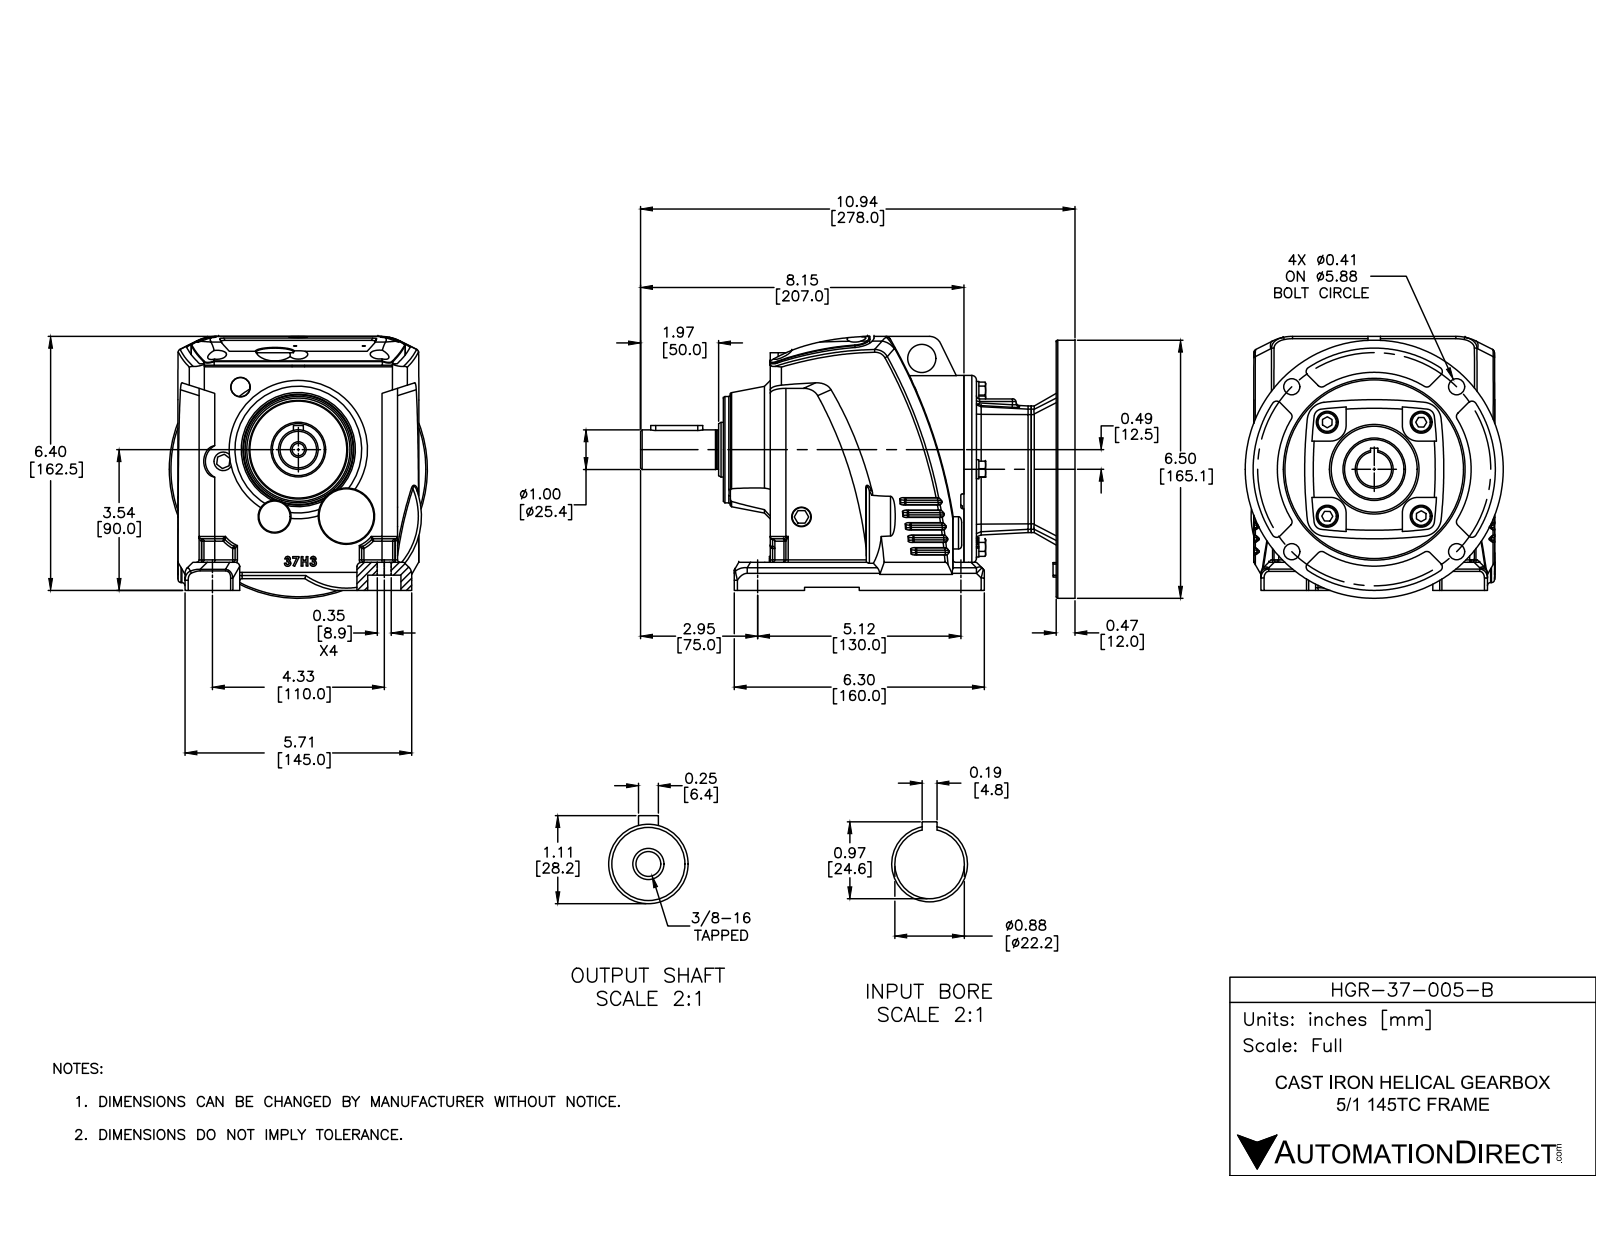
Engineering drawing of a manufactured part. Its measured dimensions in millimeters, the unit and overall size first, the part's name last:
Units: millimetres
Overall size (bounding box): 278 × 167.5 × 165.1
Round holes (diameter × count): ⌀12 ×6, ⌀10.3 ×4, ⌀14 ×4, ⌀7 ×3, ⌀2 ×2, ⌀9 ×2, ⌀10 ×2, ⌀8 ×1, ⌀13.5 ×1, ⌀18 ×1, ⌀22.2 ×1, ⌀35 ×1
Round bosses / shafts (diameter × count): ⌀13 ×7, ⌀12.2 ×4, ⌀165.1 ×1, ⌀120 ×1, ⌀68 ×1, ⌀62 ×1, ⌀55 ×1, ⌀35 ×1
Partial cylindrical surfaces — rounded edges, fillets, slot ends (radius × count): R1.5 ×43, R3 ×19, R2 ×18, R10 ×10, R5 ×8, R8 ×5, R4 ×4, R7 ×4
Main face-to-face distances: 7, 16, 59, 28, 190, 43, 183, 8, 23, 66
Hole centre spacings: 32.1, 42.5, 74.6, 85.9, 85.9, 117.1, 34.8, 47.4
Volume: 3 066 000 mm³ · Surface area: 308 500 mm²
Bodies: 28 solids, 1025 faces (348 planar, 289 cylindrical, 388 other)
Part name (STEP PRODUCT): HGR-37-005-B
STEP written by: SolidWorks 2015 (CONFIG_CONTROL_DESIGN)
